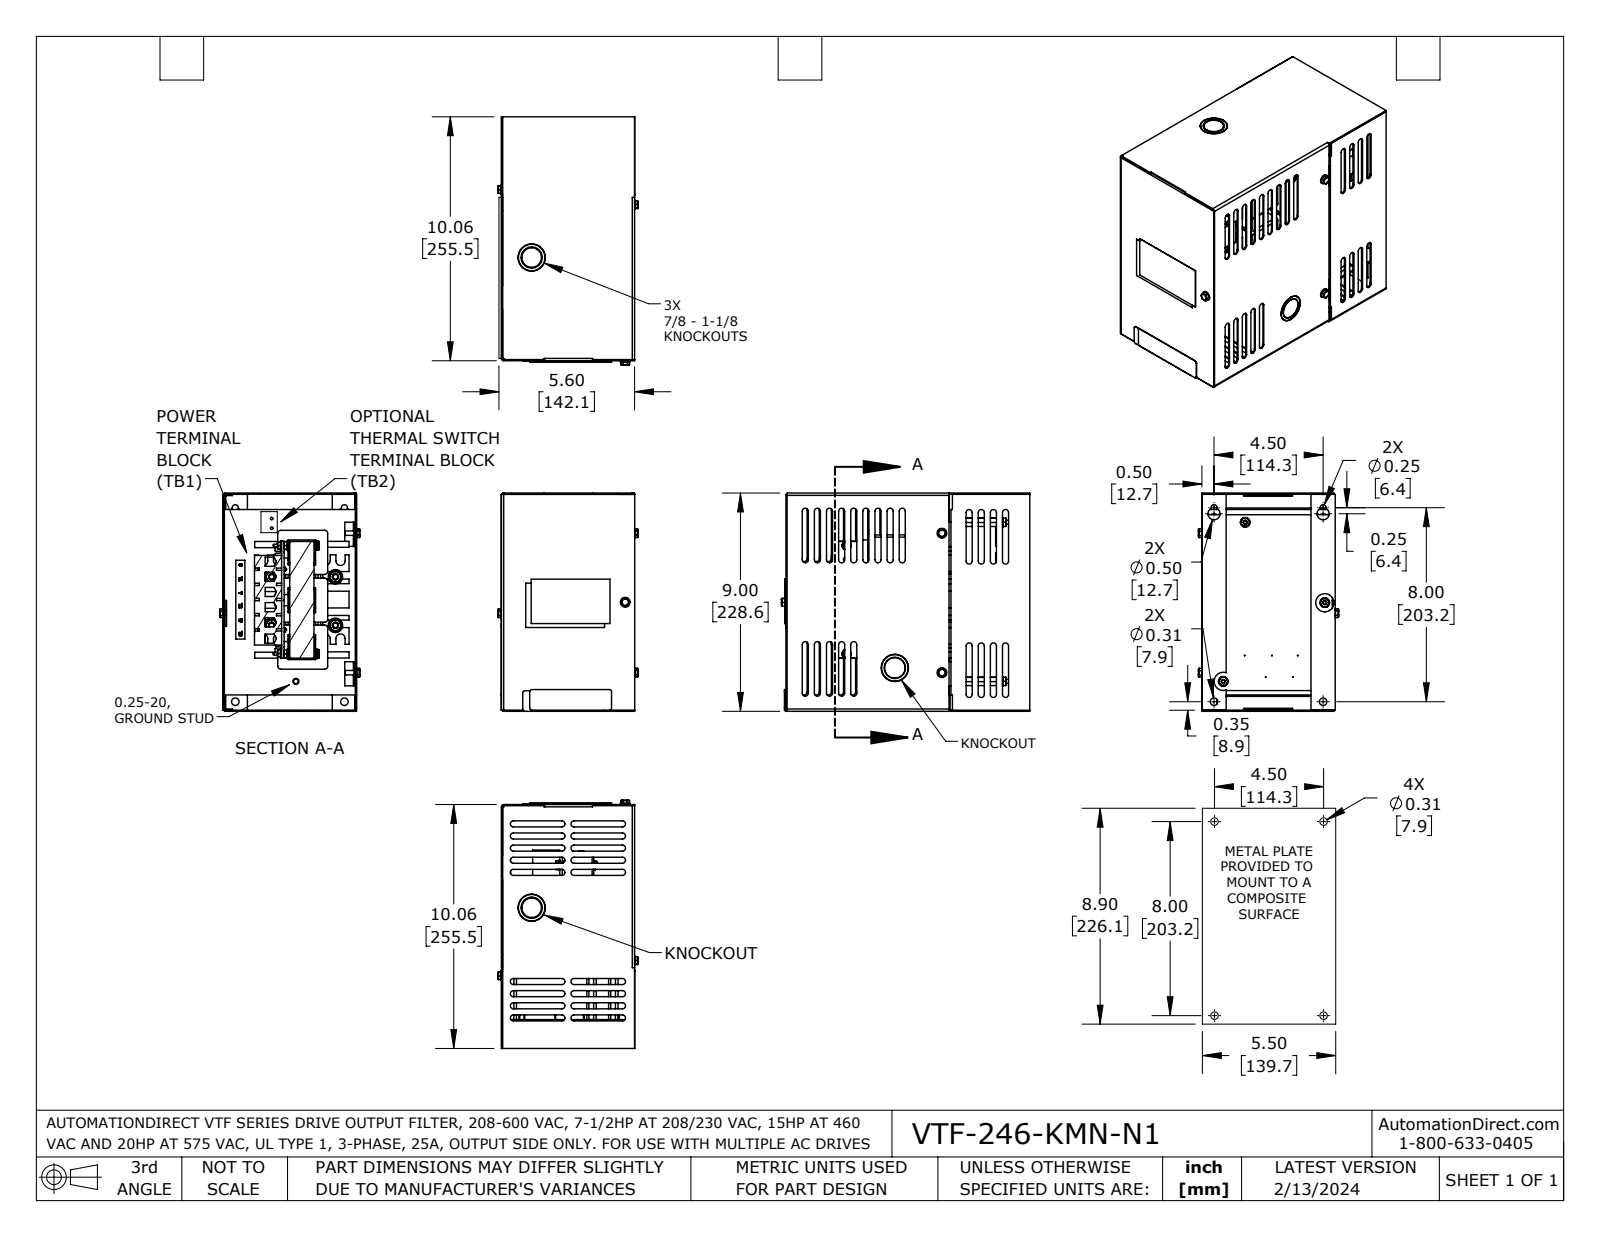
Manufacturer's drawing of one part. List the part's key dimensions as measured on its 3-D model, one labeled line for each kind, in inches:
Part name (STEP PRODUCT): VTF-246-KMN-N1
STEP written by: SolidWorks 2021 (AUTOMOTIVE_DESIGN)
Units: inches
Bodies: 42 solids, 2962 faces (1795 planar, 732 cylindrical, 435 other)
Overall size (bounding box): 10.244 × 9 × 5.787
Volume: 51.11 in³ · Surface area: 1 219 in²
Round holes (diameter × count): ⌀0.276 ×16, ⌀0.104 ×7, ⌀0.31 ×7, ⌀0.03 ×6, ⌀0.14 ×6, ⌀0.164 ×5, ⌀0.186 ×5, ⌀0.16 ×4, ⌀0.196 ×4, ⌀0.25 ×4, ⌀0.165 ×3, ⌀0.19 ×3
Round bosses / shafts (diameter × count): ⌀0.25 ×5, ⌀0.38 ×4, ⌀0.181 ×4, ⌀0.19 ×2, ⌀0.164 ×2, ⌀0.15 ×2, ⌀1.125 ×1
Partial cylindrical surfaces — rounded edges, fillets, slot ends (radius × count): R0.125 ×130, R0.03 ×68, R0.05 ×20, R0.155 ×17, R0.09 ×14, R0.019 ×12, R0.039 ×12, R0.049 ×12
Main face-to-face distances: 0.048, 0.059, 8.952, 0.047, 2, 5.448, 5.495, 5.4, 5.447, 0.05
Hole centre spacings: 0.465, 3.555, 1.24, 1.25, 1.328, 1.939, 0.378, 0.381
